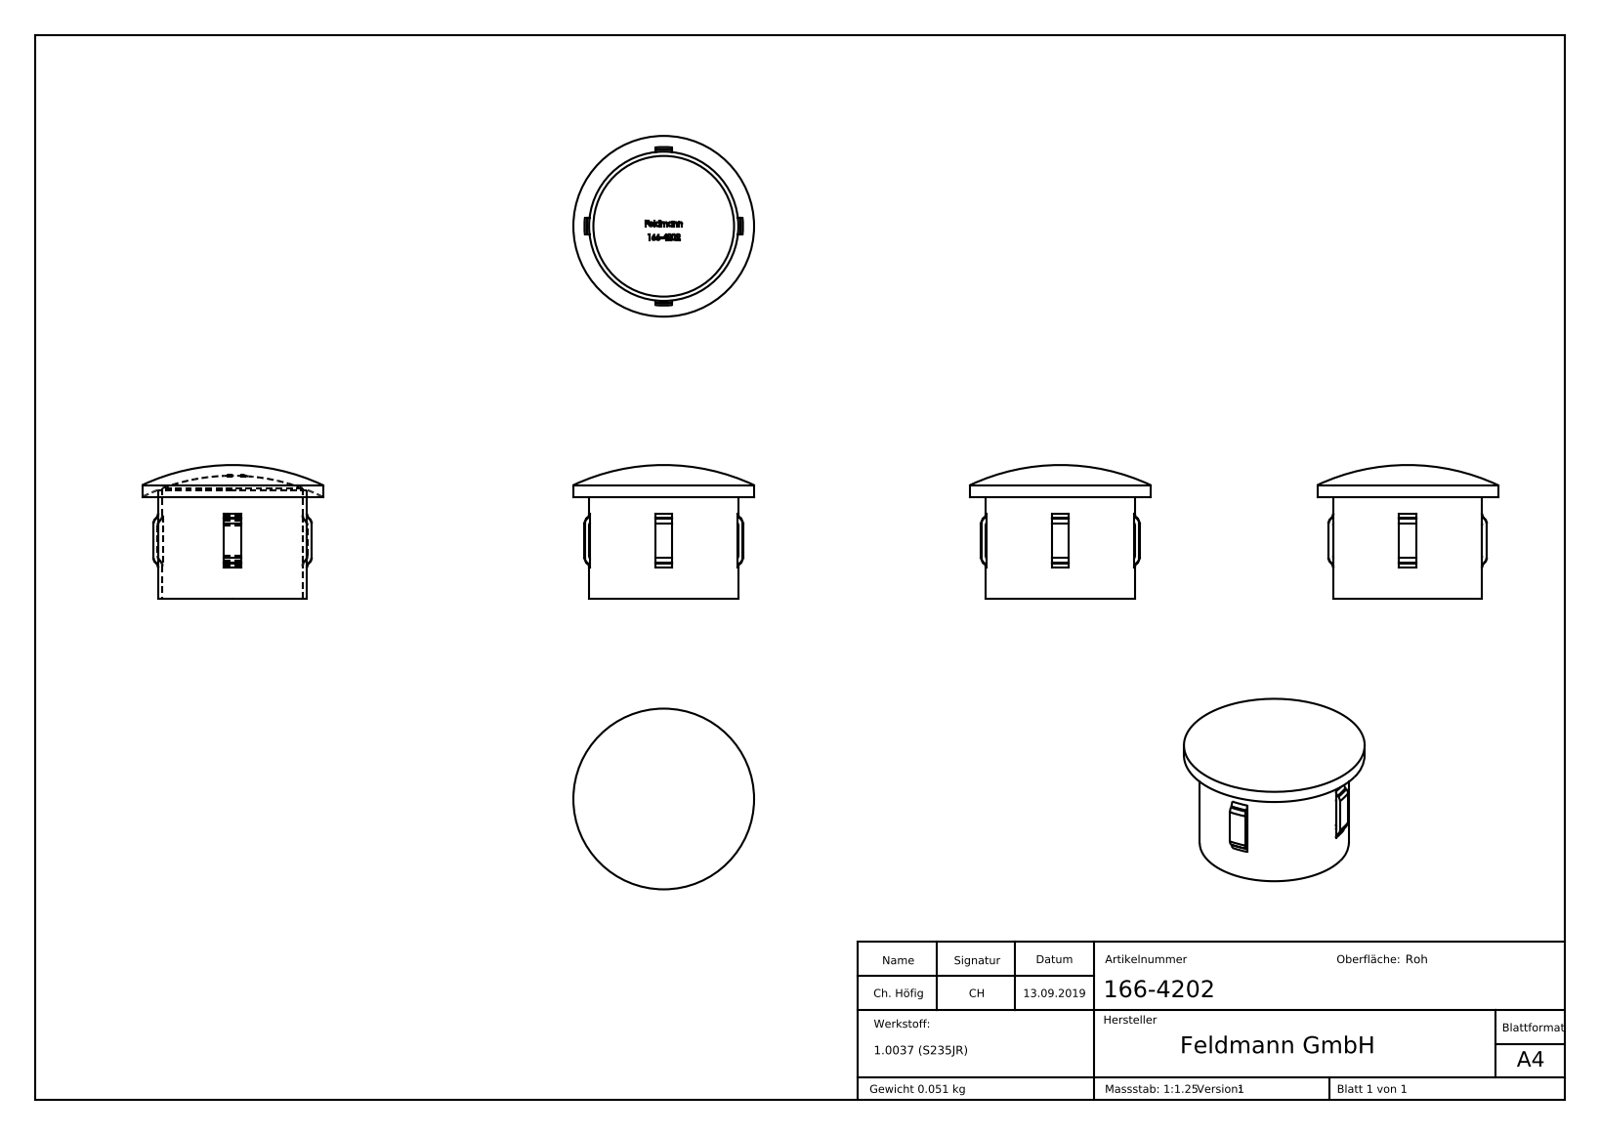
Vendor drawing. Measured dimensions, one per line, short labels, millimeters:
name: 166-4202
written by: SolidWorks 2015 (CONFIG_CONTROL_DESIGN)
unit: mm
bodies: 1 solid, 313 faces (112 planar, 16 cylindrical, 185 other)
size: 42.4 × 42.4 × 31.4
volume: 6 479 mm³; area: 9 027 mm²
holes: 1× ⌀33
bosses: 1× ⌀42.4, 1× ⌀35
rounds: 1× R17.6, 1× R18.6
face distances: 4, 2, 2.97, 2.85, 1.2, 0.39, 1.26, 1.48, 1.41, 3.66
